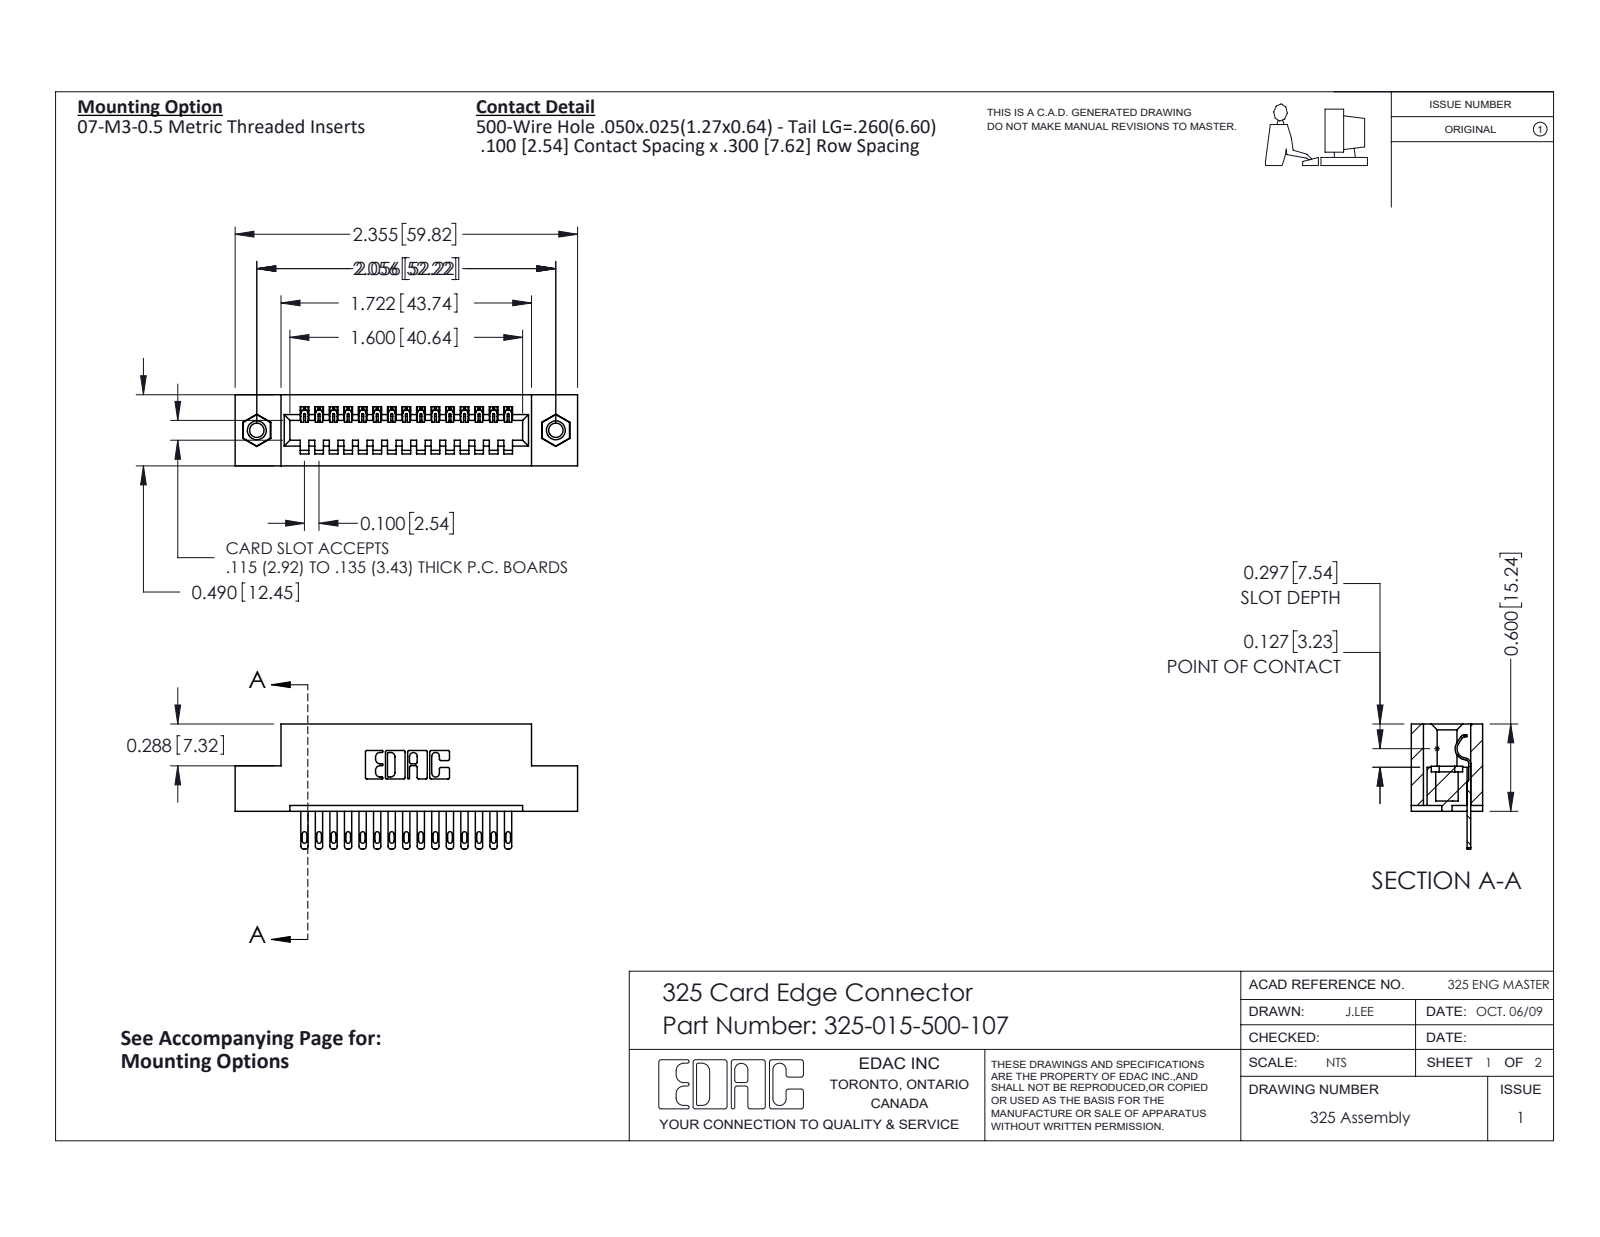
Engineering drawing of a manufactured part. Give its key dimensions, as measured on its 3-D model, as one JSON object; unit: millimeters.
{"part_name": "325-015-500-107; 325 Part_TI; 325-292-001_325-293-100; 345-250-001_345-250-005-103", "step_written_by": "SolidWorks 2016 (CONFIG_CONTROL_DESIGN)", "units": "millimeters", "bodies": {"solids": 18, "faces": 984, "planar": 642, "cylindrical": 326, "other": 16}, "overall_size": [59.8, 21.8, 12.4], "volume_mm3": 7370, "surface_area_mm2": 7665, "round_holes": [[2.5, 2], [3.2, 2], [4.1, 2]], "round_bosses_or_shafts": [[3.9, 2]], "partial_cylinders_radius": [[0.2, 30], [0.4, 30], [0.5, 30], [0.3, 22], [0.2, 6], [0.8, 6], [0.7, 3], [0.4, 1]], "face_to_face_distances": [2.1, 10.3, 7.6, 12.4, 2.7, 9.7, 0.6, 1, 2.5, 15.2], "hole_center_spacings": [52.2]}
